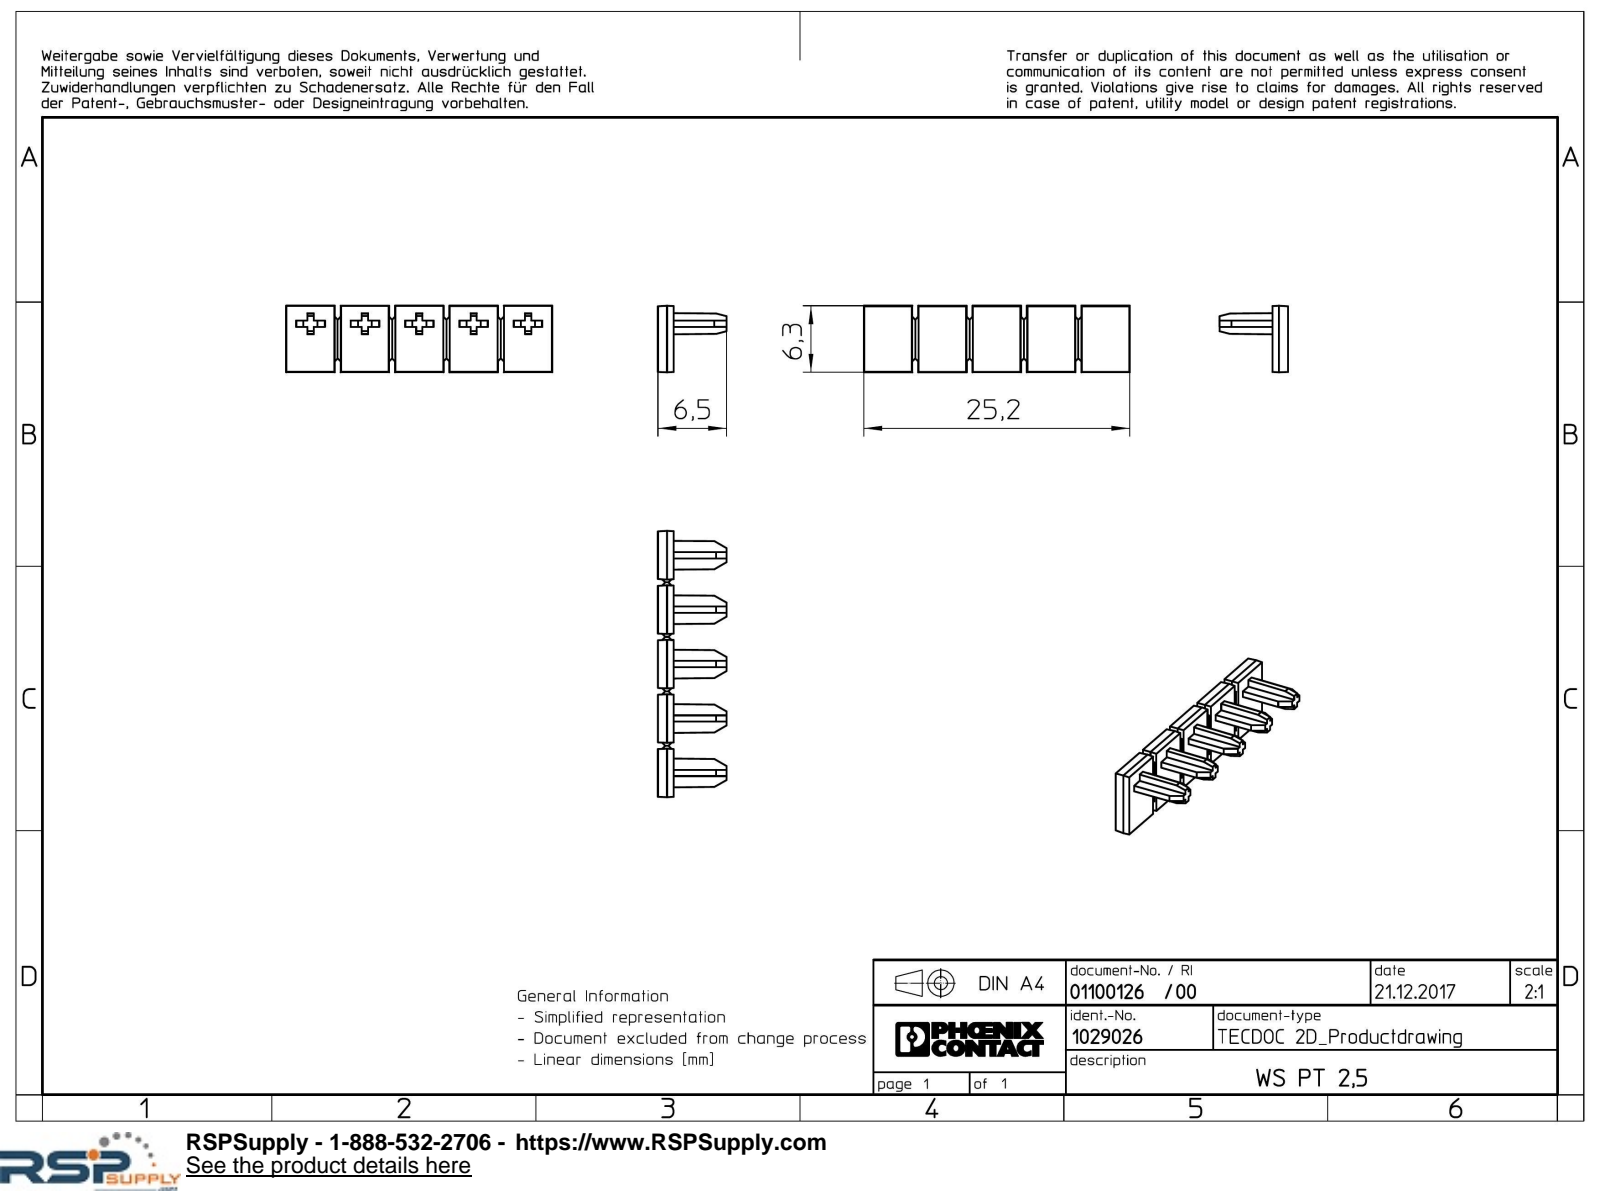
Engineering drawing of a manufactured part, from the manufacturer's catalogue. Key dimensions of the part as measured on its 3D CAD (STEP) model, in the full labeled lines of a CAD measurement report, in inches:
Part name (STEP PRODUCT): WS_PT_2.5-select
STEP written by: Creo Elements/Direct Modeling 18.1I 14-Aug-2016 (C) Parametric Technology GmbH (AUTOMOTIVE_DESIGN)
Units: inches
Bodies: 1 solid, 167 faces (167 planar, 0 cylindrical, 0 other)
Overall size (bounding box): 0.992 × 0.256 × 0.248
Volume: 0.017 in³ · Surface area: 1.02 in²
Main face-to-face distances: 0.059, 0.203, 0.024, 0.406, 0.608, 0.405, 0.226, 0.179, 0.202, 0.143
